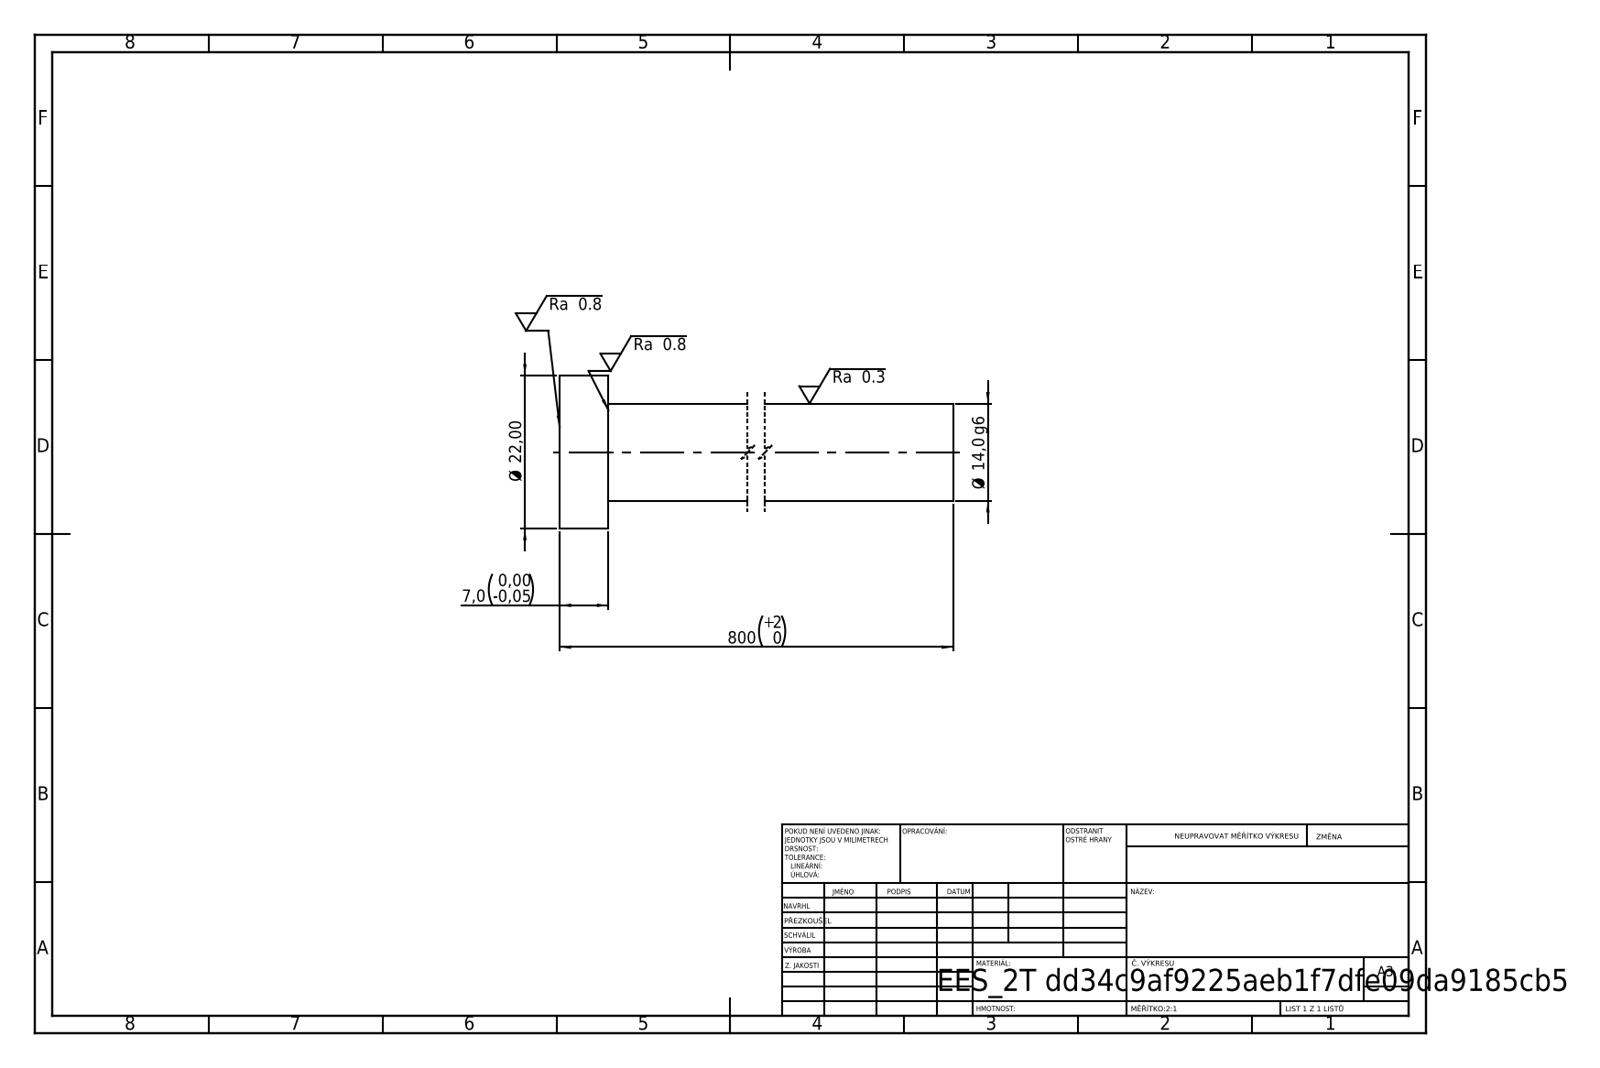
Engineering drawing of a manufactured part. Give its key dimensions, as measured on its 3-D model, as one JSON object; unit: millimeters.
{"step_written_by": "SolidWorks 2019 (CONFIG_CONTROL_DESIGN)", "units": "millimeters", "bodies": {"solids": 1, "faces": 7, "planar": 3, "cylindrical": 4, "other": 0}, "overall_size": [800, 22, 22], "volume_mm3": 124734, "surface_area_mm2": 36122, "round_bosses_or_shafts": [[22, 1], [14, 1]], "face_to_face_distances": [7, 800, 793]}
